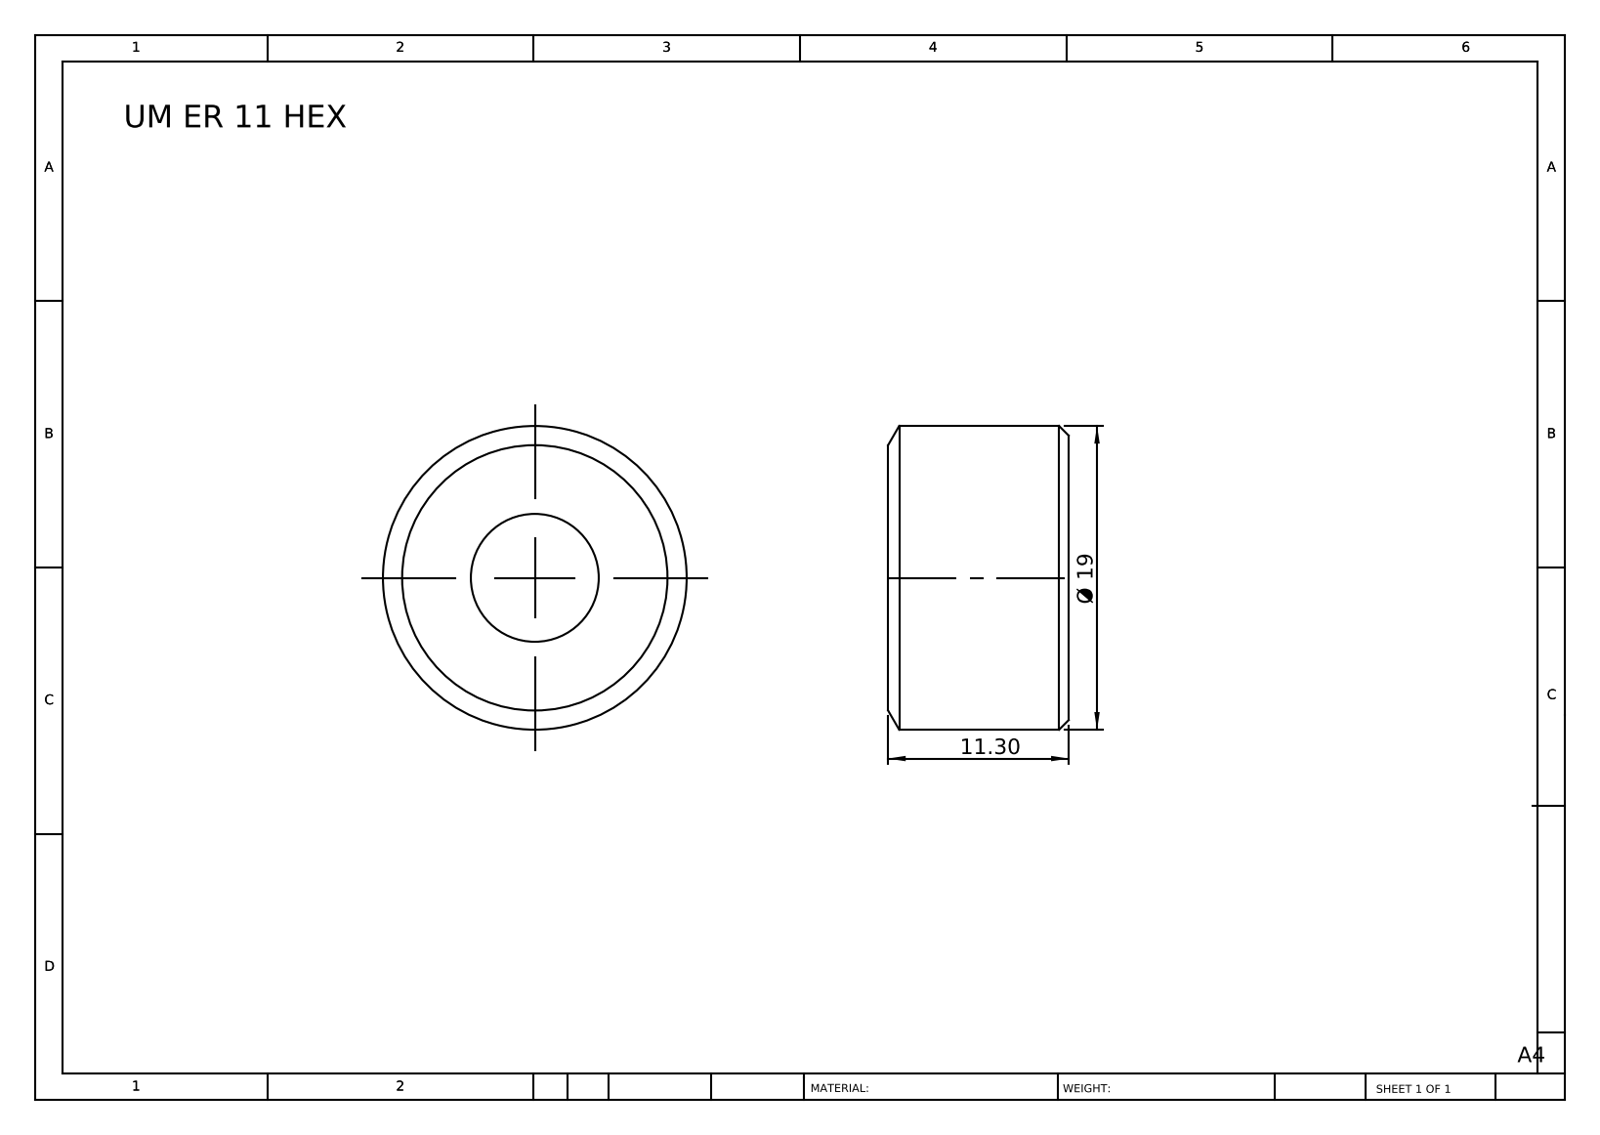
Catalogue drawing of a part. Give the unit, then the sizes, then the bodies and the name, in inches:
Units: inches
Overall size (bounding box): 0.748 × 0.748 × 0.445
Round holes (diameter × count): ⌀0.315 ×1
Round bosses / shafts (diameter × count): ⌀0.748 ×1
Main face-to-face distances: 0.445
Volume: 0.159 in³ · Surface area: 2.128 in²
Bodies: 1 solid, 10 faces (2 planar, 4 cylindrical, 4 other)
Part name (STEP PRODUCT): UM ER 11 HEX
STEP written by: SolidWorks 2014 (CONFIG_CONTROL_DESIGN)
